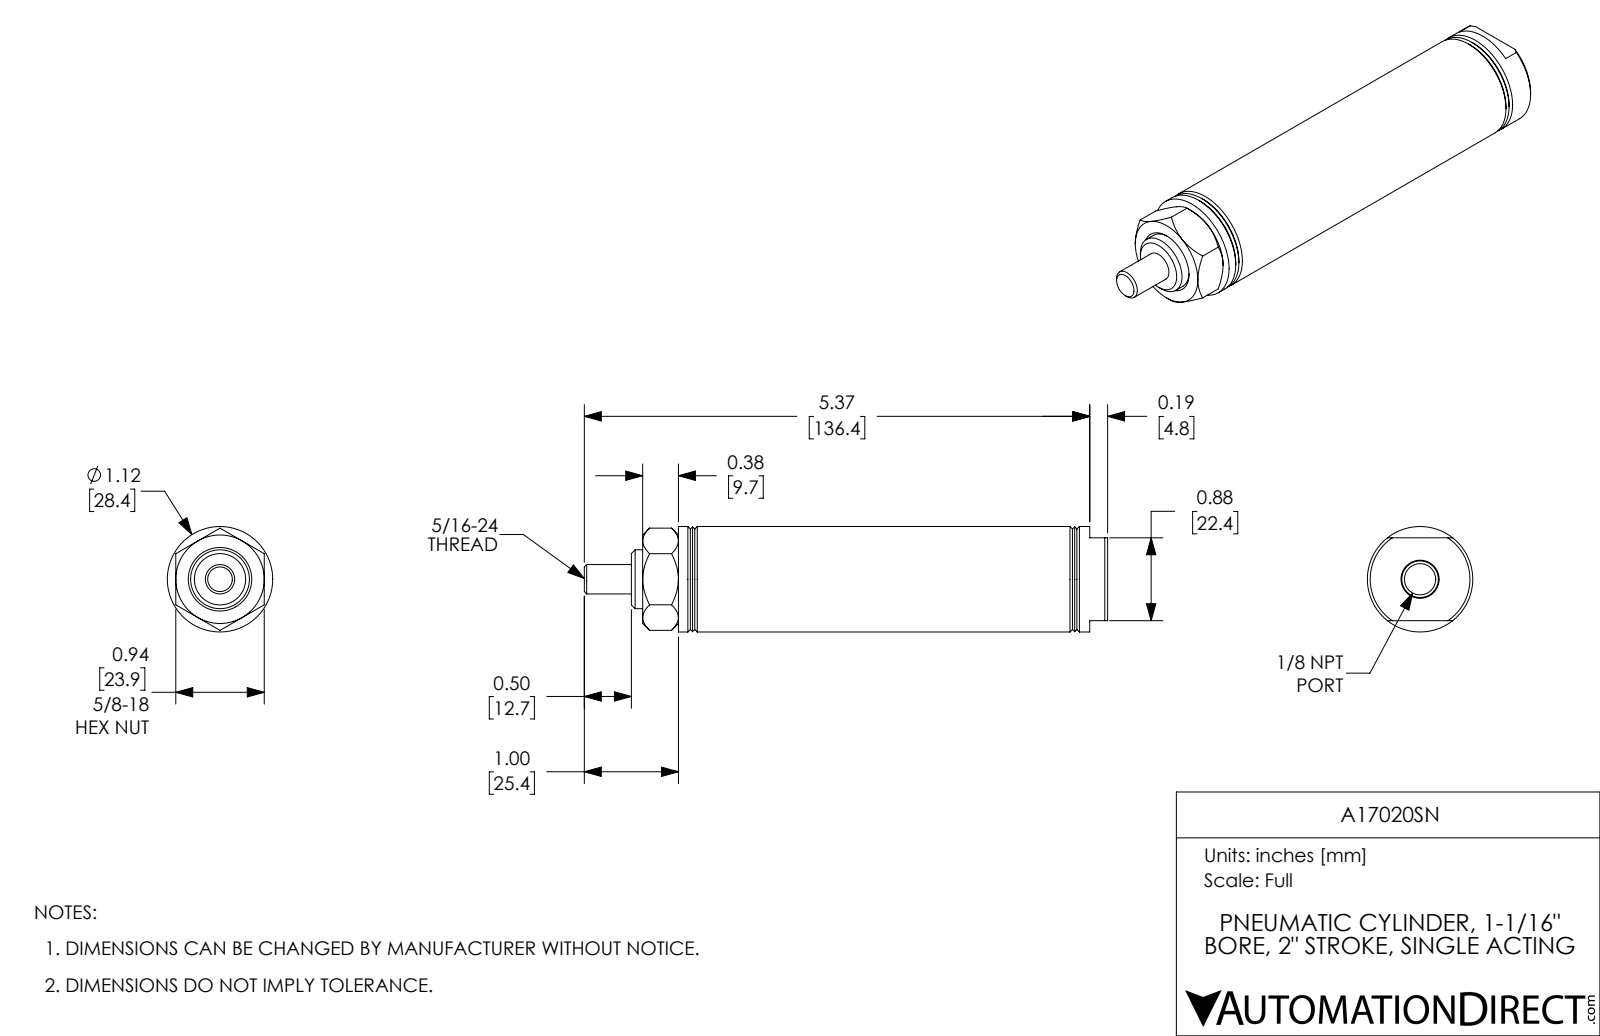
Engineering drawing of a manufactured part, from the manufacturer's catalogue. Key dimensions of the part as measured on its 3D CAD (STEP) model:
Part name (STEP PRODUCT): A17020SN; A17020SN-Rod; A17020SN_Mounting Nut_D-9; A17020SN-MainBody
STEP written by: SolidWorks 2017 (AUTOMOTIVE_DESIGN)
Units: inches
Bodies: 3 solids, 82 faces (21 planar, 20 cylindrical, 41 other)
Overall size (bounding box): 5.56 × 1.12 × 1.12
Volume: 3.1 in³ · Surface area: 41.69 in²
Round holes (diameter × count): ⌀0.312 ×1, ⌀0.332 ×1, ⌀0.625 ×1, ⌀1.063 ×1
Round bosses / shafts (diameter × count): ⌀1.12 ×1
Main face-to-face distances: 3.53, 1.03, 0.5, 1.53, 2.5, 2, 3.03, 4.56, 0.94, 4.94
